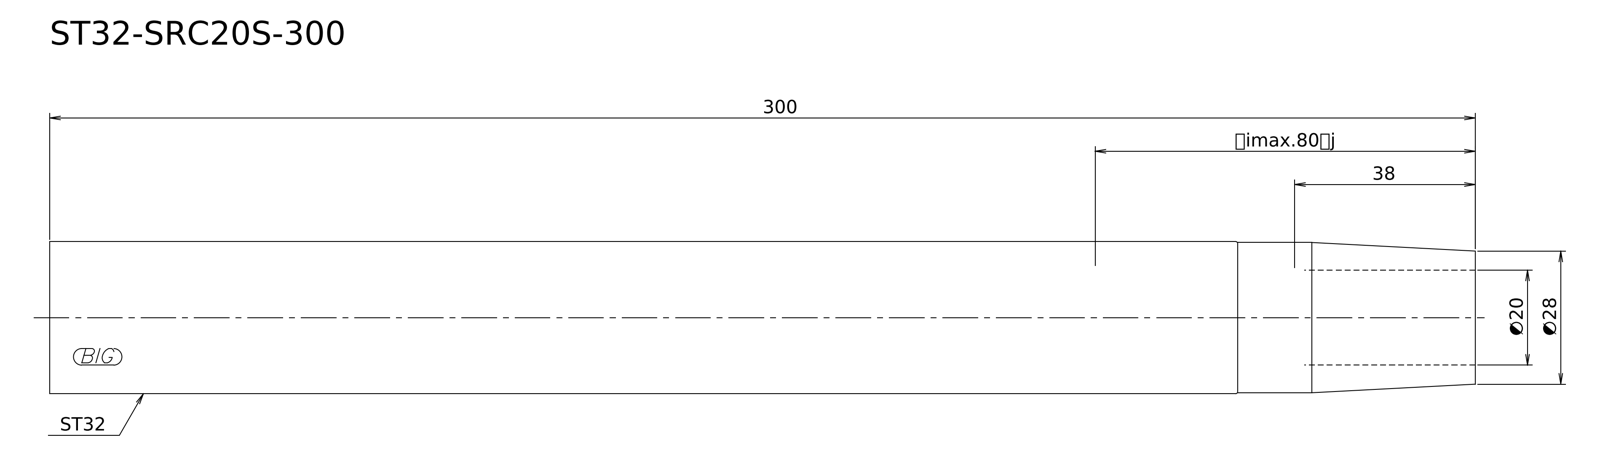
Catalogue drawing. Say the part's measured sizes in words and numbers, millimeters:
Its 3-D file was written by "Kubotek KeyCreator V8.5.1 (14335) (CONFIG_CONTROL_DESIGN)". It is 1 solid with 6 faces: 2 planar, 2 cylindrical and 2 other. Overall it measures 300 by 32 by 32 millimeters. Its volume is 237 320 cubic millimeters and its surface area 31 332 square millimeters. Round bosses or shafts: 1 of diameter 32, 1 of diameter 31.6. The main face-to-face distances are 300.
